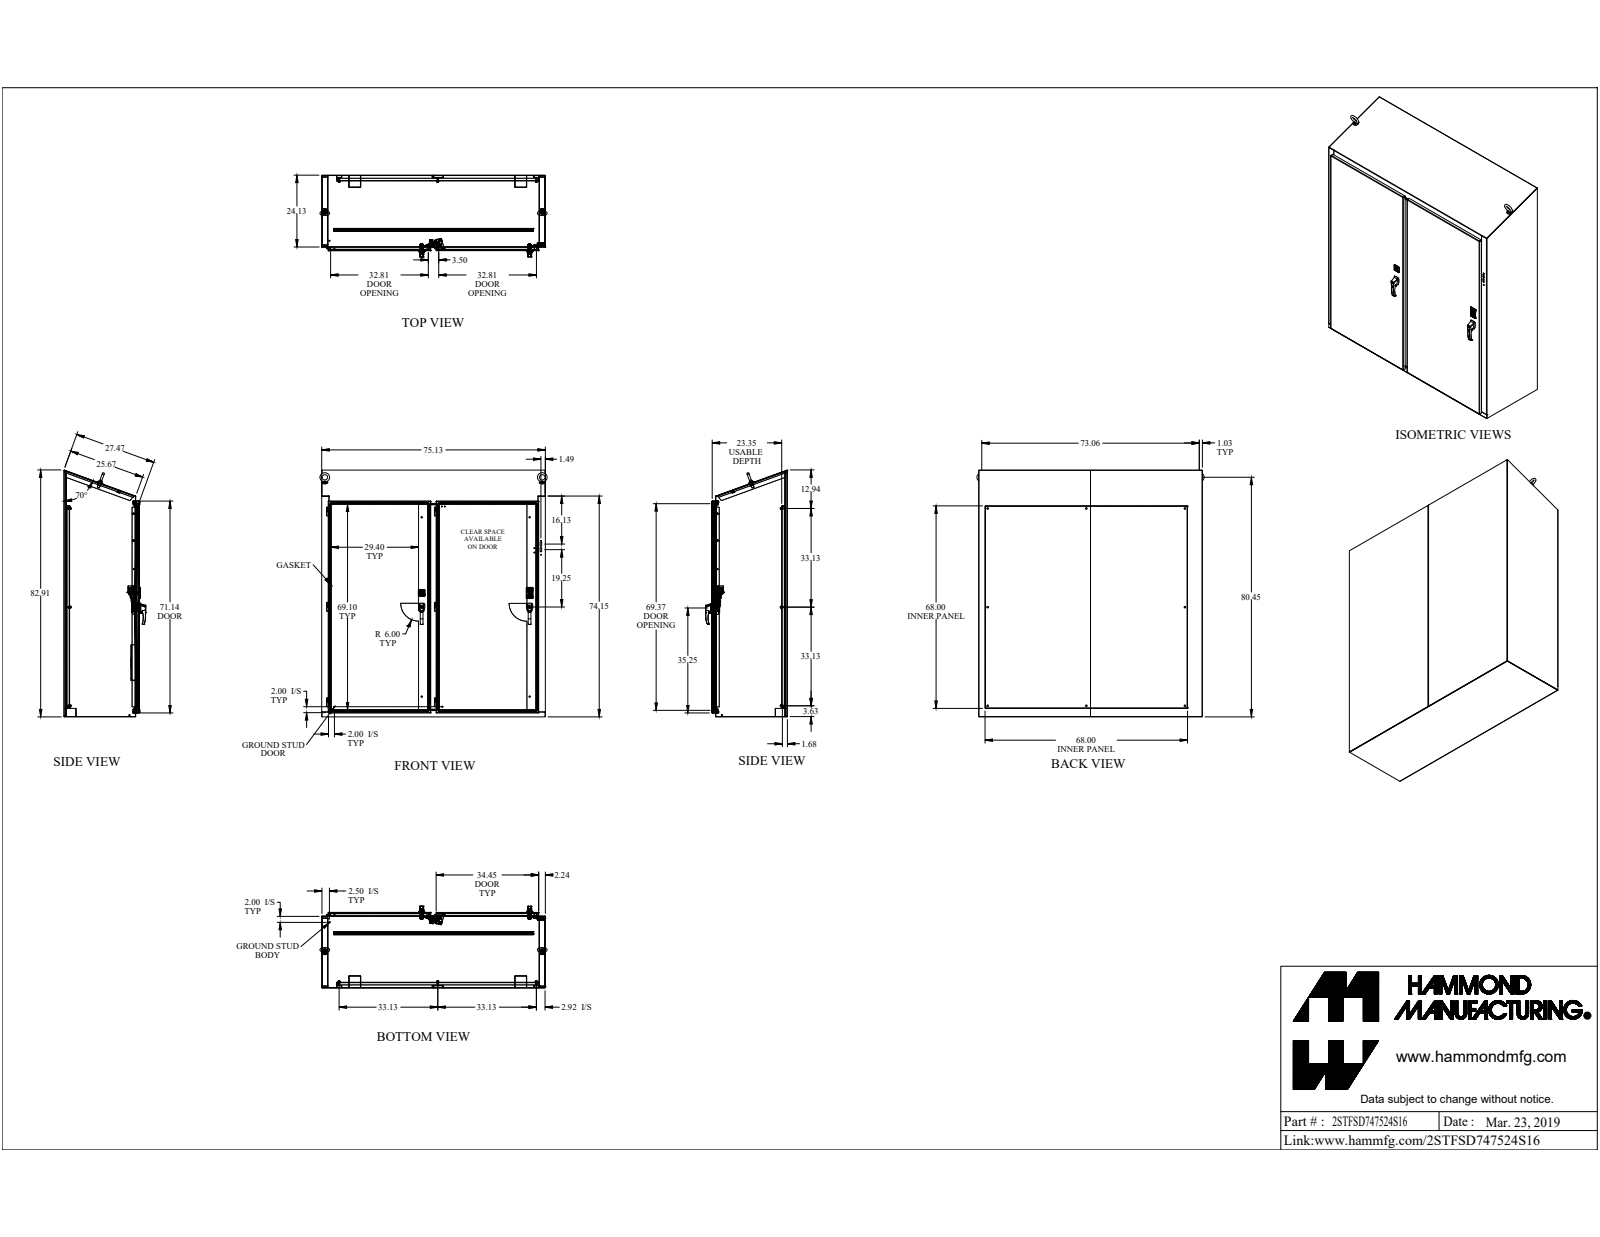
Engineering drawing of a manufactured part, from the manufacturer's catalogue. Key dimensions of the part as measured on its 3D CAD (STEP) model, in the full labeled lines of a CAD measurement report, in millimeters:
Part name (STEP PRODUCT): 2STFSD747524S16
STEP written by: SolidWorks 2019 (CONFIG_CONTROL_DESIGN)
Units: millimetres
Bodies: 210 solids, 3274 faces (1902 planar, 992 cylindrical, 380 other)
Overall size (bounding box): 2104.6 × 1938.2 × 698.3
Volume: 46 640 000 mm³ · Surface area: 36 700 000 mm²
Round holes (diameter × count): ⌀5 ×11, ⌀6.4 ×9, ⌀7.1 ×9, ⌀7.8 ×9, ⌀8.9 ×8, ⌀14.3 ×8, ⌀6.5 ×6, ⌀8 ×6, ⌀11.3 ×6, ⌀7.1 ×4, ⌀7.2 ×4, ⌀9.5 ×4
Round bosses / shafts (diameter × count): ⌀6.4 ×18, ⌀25.4 ×14, ⌀16.5 ×9, ⌀9.5 ×9, ⌀15.9 ×8, ⌀8.4 ×8, ⌀19.1 ×6, ⌀12.7 ×5
Partial cylindrical surfaces — rounded edges, fillets, slot ends (radius × count): R3.2 ×64, R1.2 ×36, R3.6 ×36, R12.7 ×34, R0.8 ×28, R1.5 ×27, R6.4 ×24, R0.3 ×20
Main face-to-face distances: 2.4, 2.4, 641.5, 3.2, 46, 48.4, 42.8, 45.3, 1905.8, 0.6
Hole centre spacings: 1855.7, 1881.4, 1682.8, 841.4, 841.4, 25.4, 920.9, 1189.9
